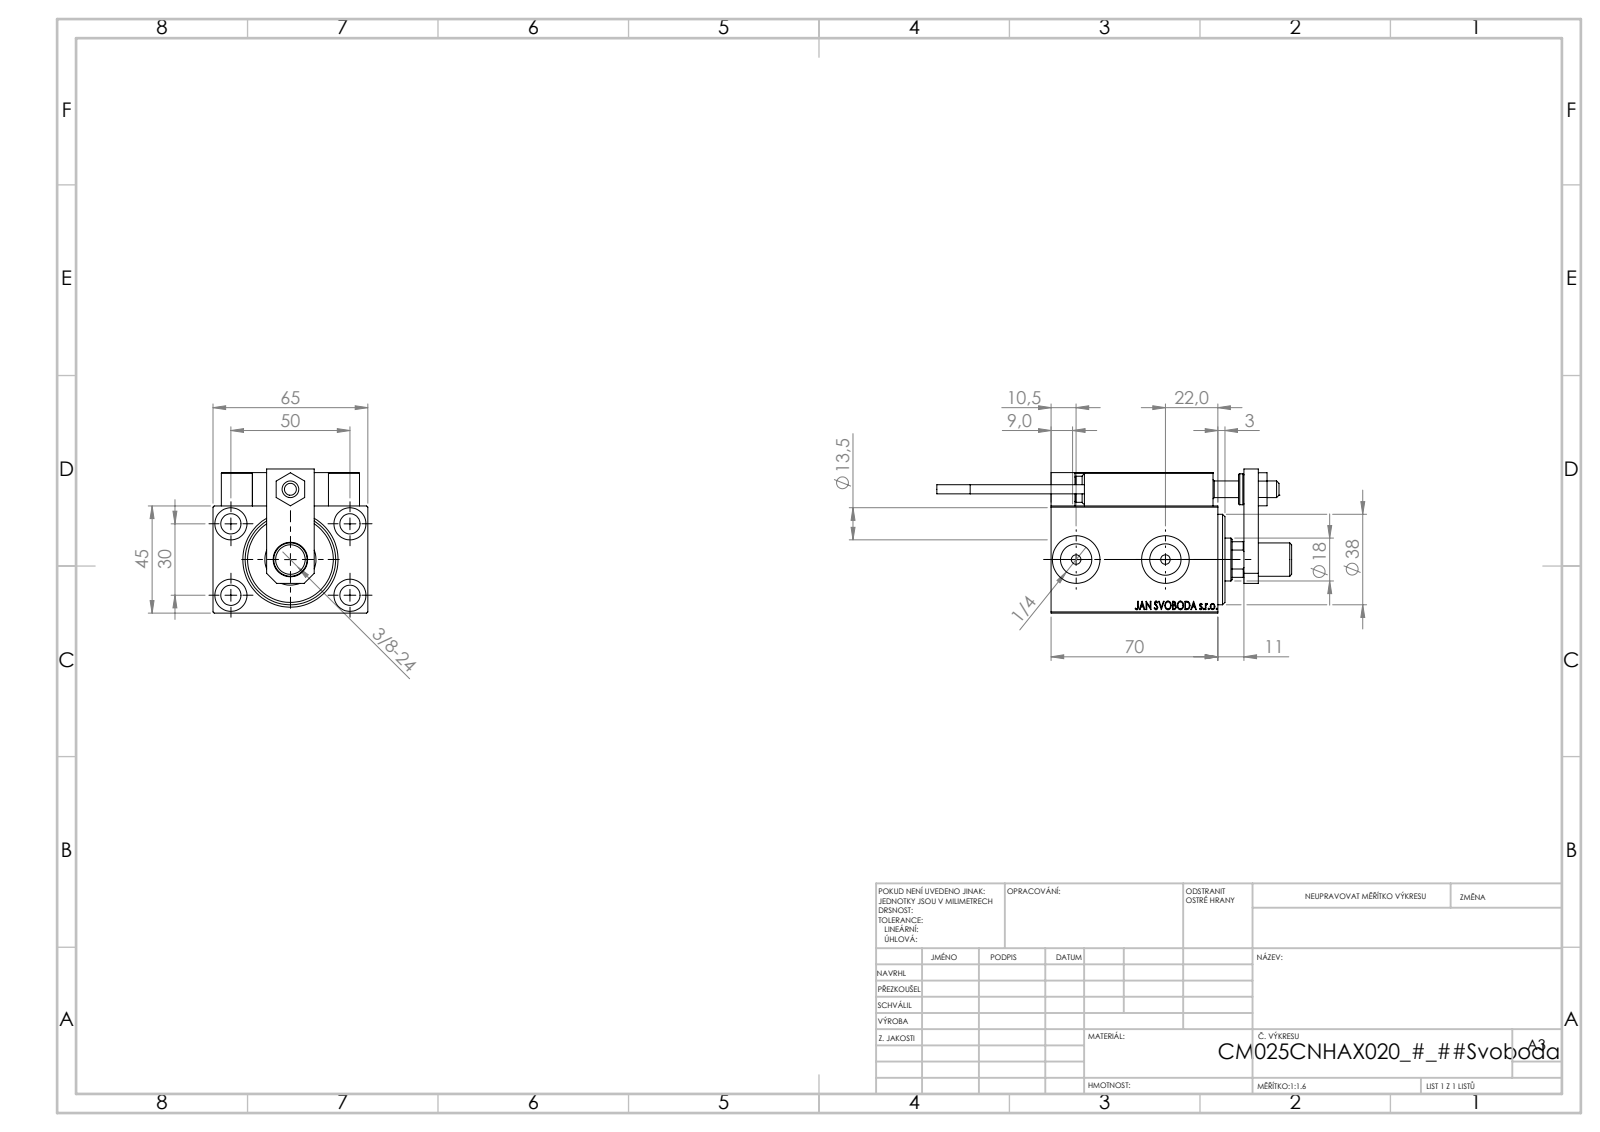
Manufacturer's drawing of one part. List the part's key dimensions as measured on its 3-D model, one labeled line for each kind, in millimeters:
Part name (STEP PRODUCT): NUT_D12; SWITCH DIM B,W; KONCOVKA; V450CM_MALE_METRIC (+8 more)
STEP written by: SolidWorks 2019 (CONFIG_CONTROL_DESIGN)
Units: millimetres
Bodies: 24 solids, 1295 faces (563 planar, 192 cylindrical, 540 other)
Overall size (bounding box): 149 × 65 × 60.5
Volume: 226 080 mm³ · Surface area: 70 361 mm²
Round holes (diameter × count): ⌀4 ×6, ⌀8 ×5, ⌀8.5 ×5, ⌀3.2 ×4, ⌀13.5 ×4, ⌀5 ×2, ⌀13.16 ×2, ⌀20 ×2, ⌀7 ×1, ⌀14.5 ×1, ⌀18 ×1, ⌀21.5 ×1
Round bosses / shafts (diameter × count): ⌀5 ×2, ⌀3.8 ×2, ⌀14 ×1, ⌀13 ×1, ⌀12 ×1, ⌀11 ×1
Partial cylindrical surfaces — rounded edges, fillets, slot ends (radius × count): R0.3 ×30, R3 ×2, R8.5 ×1
Main face-to-face distances: 45, 59, 14, 65, 6, 3, 19, 5, 13, 7
Hole centre spacings: 29.15, 11.37, 20, 22.09, 28.9, 29.59, 29.69, 30
